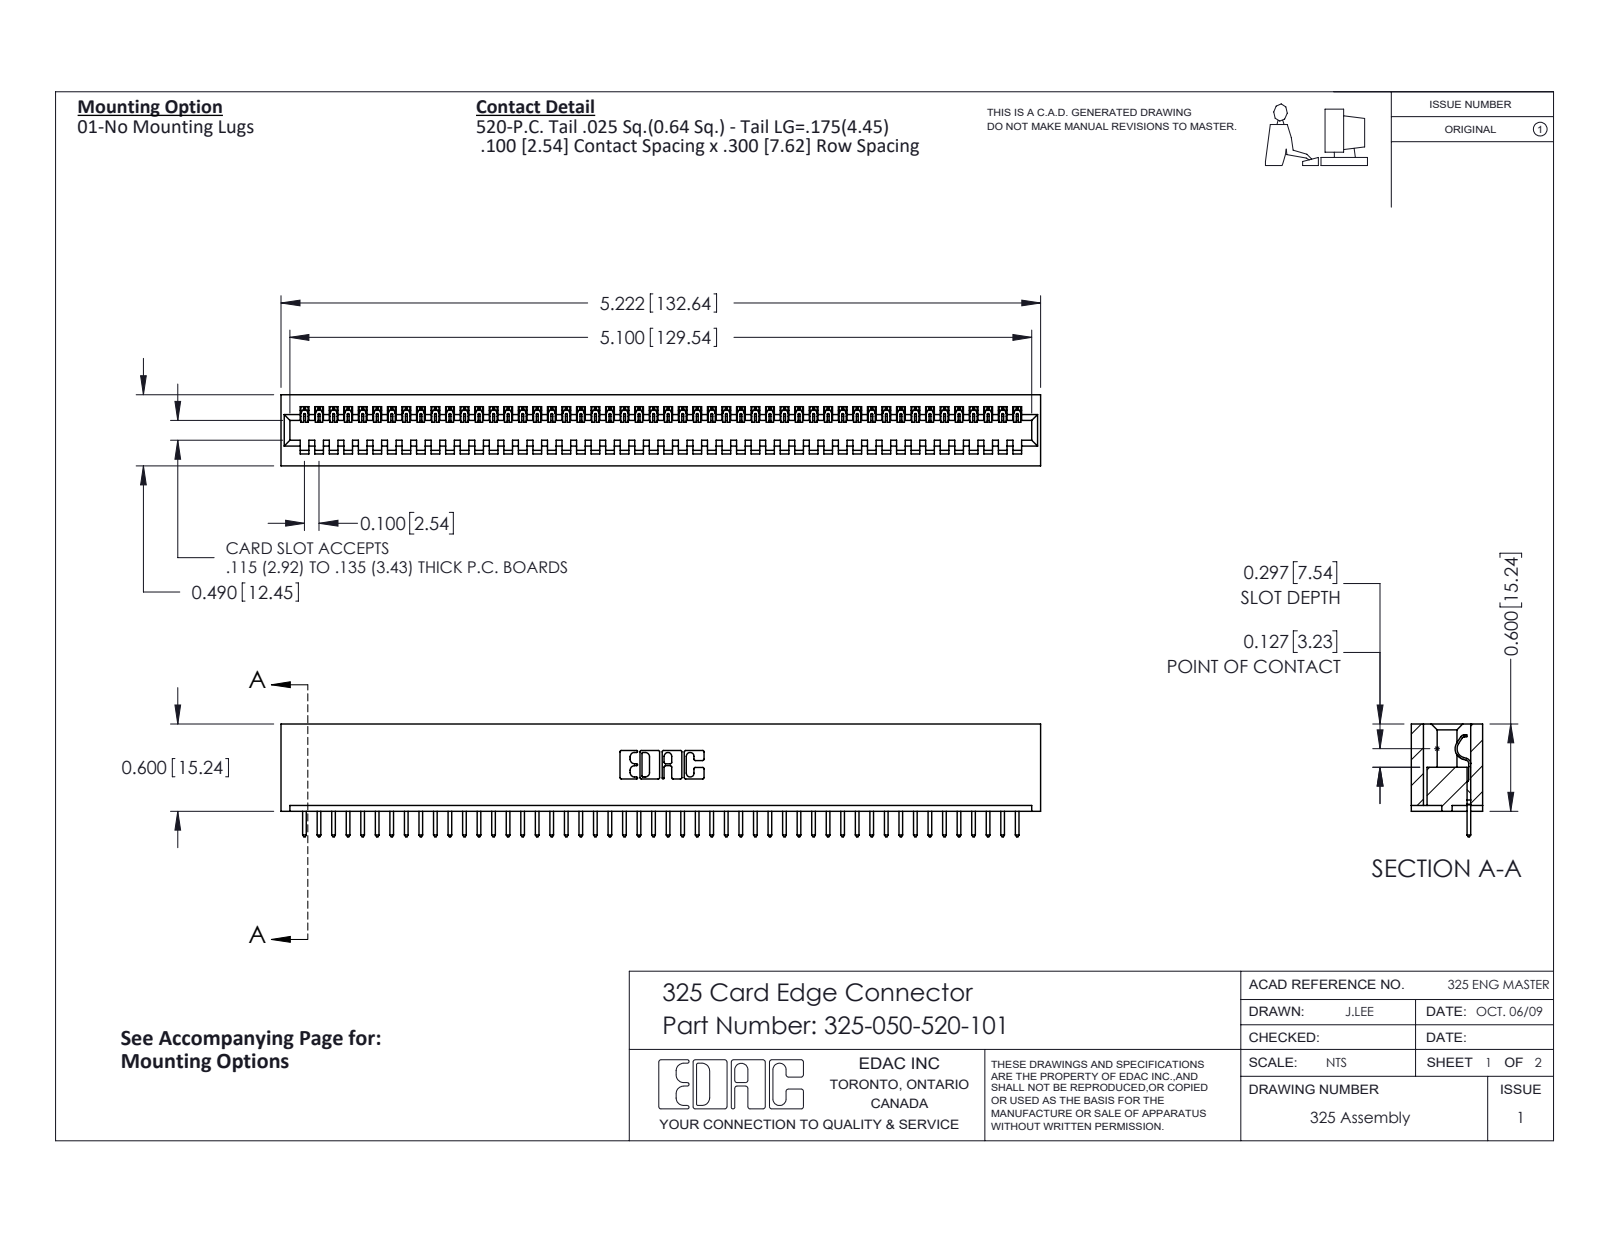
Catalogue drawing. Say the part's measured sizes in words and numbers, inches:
The part is named "325-050-520-101; 325-292-001_325-293-120; 325 Part_Lugless". Its 3-D file was written by "SolidWorks 2016 (CONFIG_CONTROL_DESIGN)". It is 51 solids with 3006 faces: 2166 planar, 840 cylindrical and 0 other. Overall it measures 5.222 by 0.775 by 0.49 inches. Its volume is 1.058 cubic inches and its surface area 29.53 square inches. Partial cylindrical surfaces (rounded edges, fillets, slot ends): 100 of radius 0.006, 100 of radius 0.01, 22 of radius 0.01, 6 of radius 0.007, 6 of radius 0.031, 3 of radius 0.026, 1 of radius 0.014, 1 of radius 0.022. The main face-to-face distances are 0.083, 0.407, 0.49, 0.3, 0.107, 0.383, 0.025, 0.325, 0.56, 0.263.
